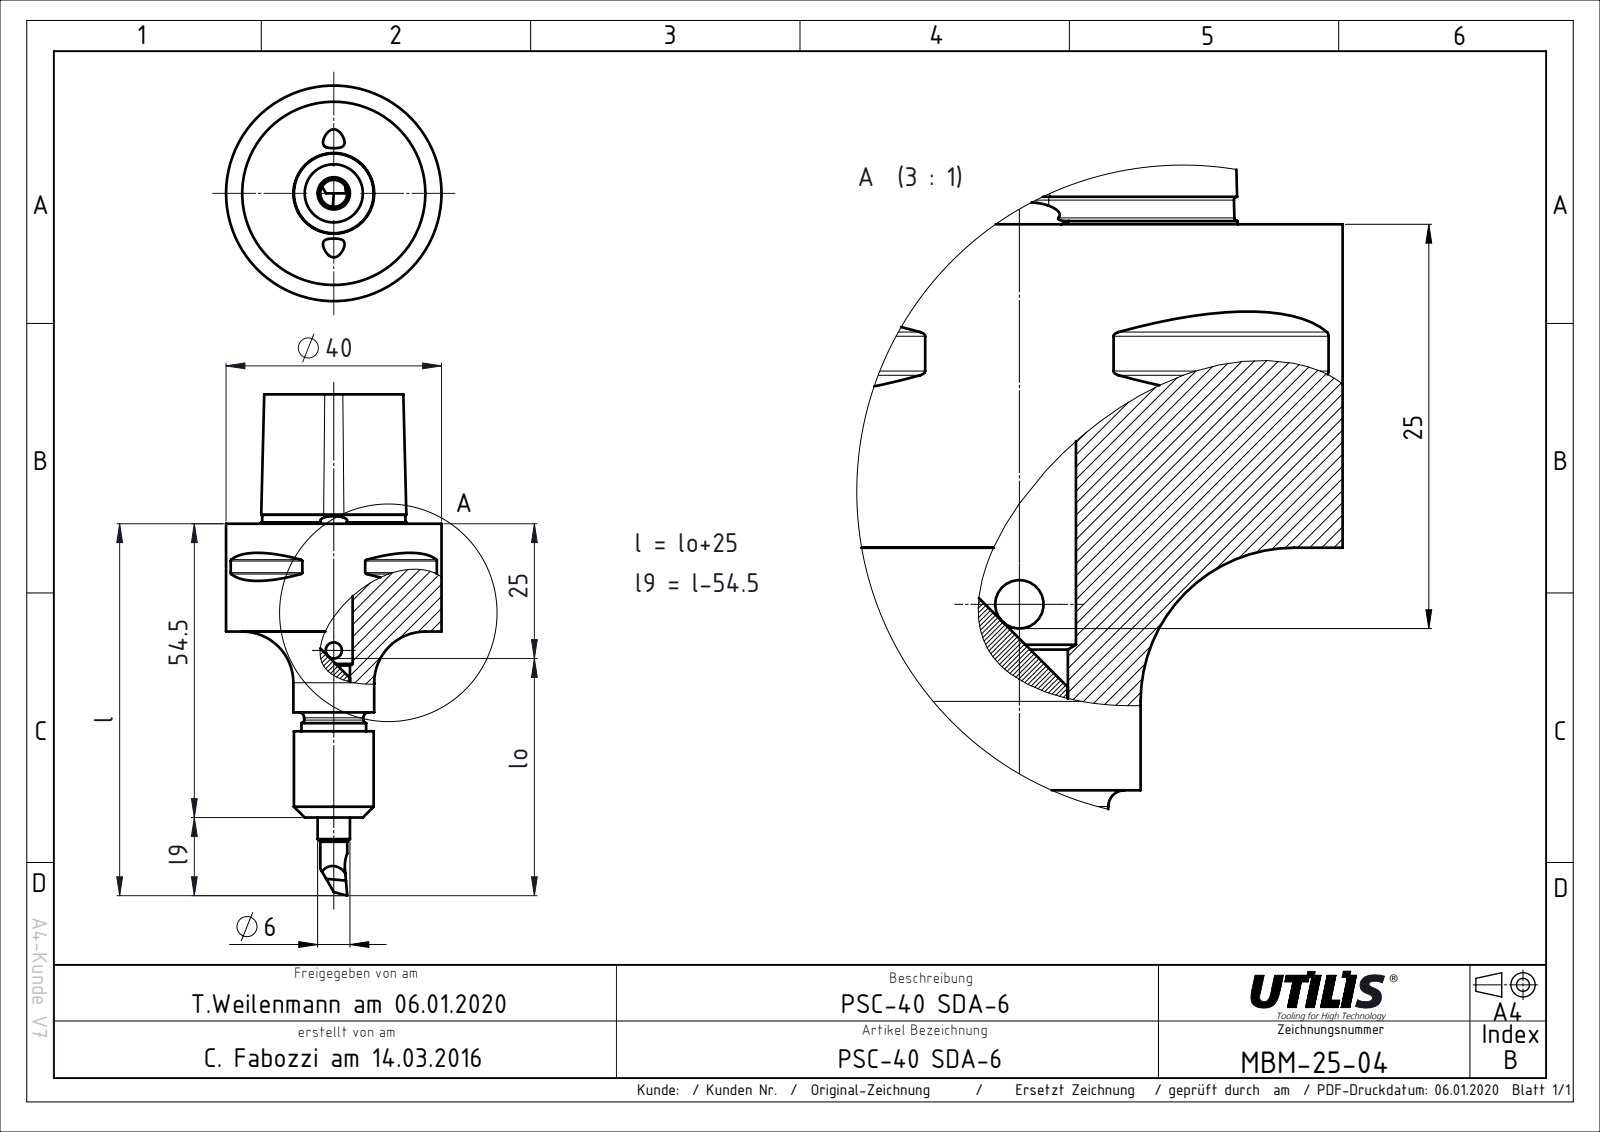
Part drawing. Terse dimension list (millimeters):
name: MBM-25 PSC40_SDA6
written by: SolidWorks 2015 (AUTOMOTIVE_DESIGN)
unit: mm
bodies: 1 solid, 137 faces (28 planar, 31 cylindrical, 78 other)
size: 93 × 40 × 40
volume: 41 839 mm³; area: 9 459 mm²
holes: 1× ⌀4.6, 1× ⌀18, 1× ⌀20
bosses: 1× ⌀40, 1× ⌀34, 1× ⌀15, 1× ⌀14.8, 1× ⌀12, 1× ⌀11, 1× ⌀6, 1× ⌀5
rounds: 8× R0.3, 1× R3
face distances: 20, 24, 44, 15.51, 35.3, 78.5, 54.5, 34.5, 62.5, 38.5
